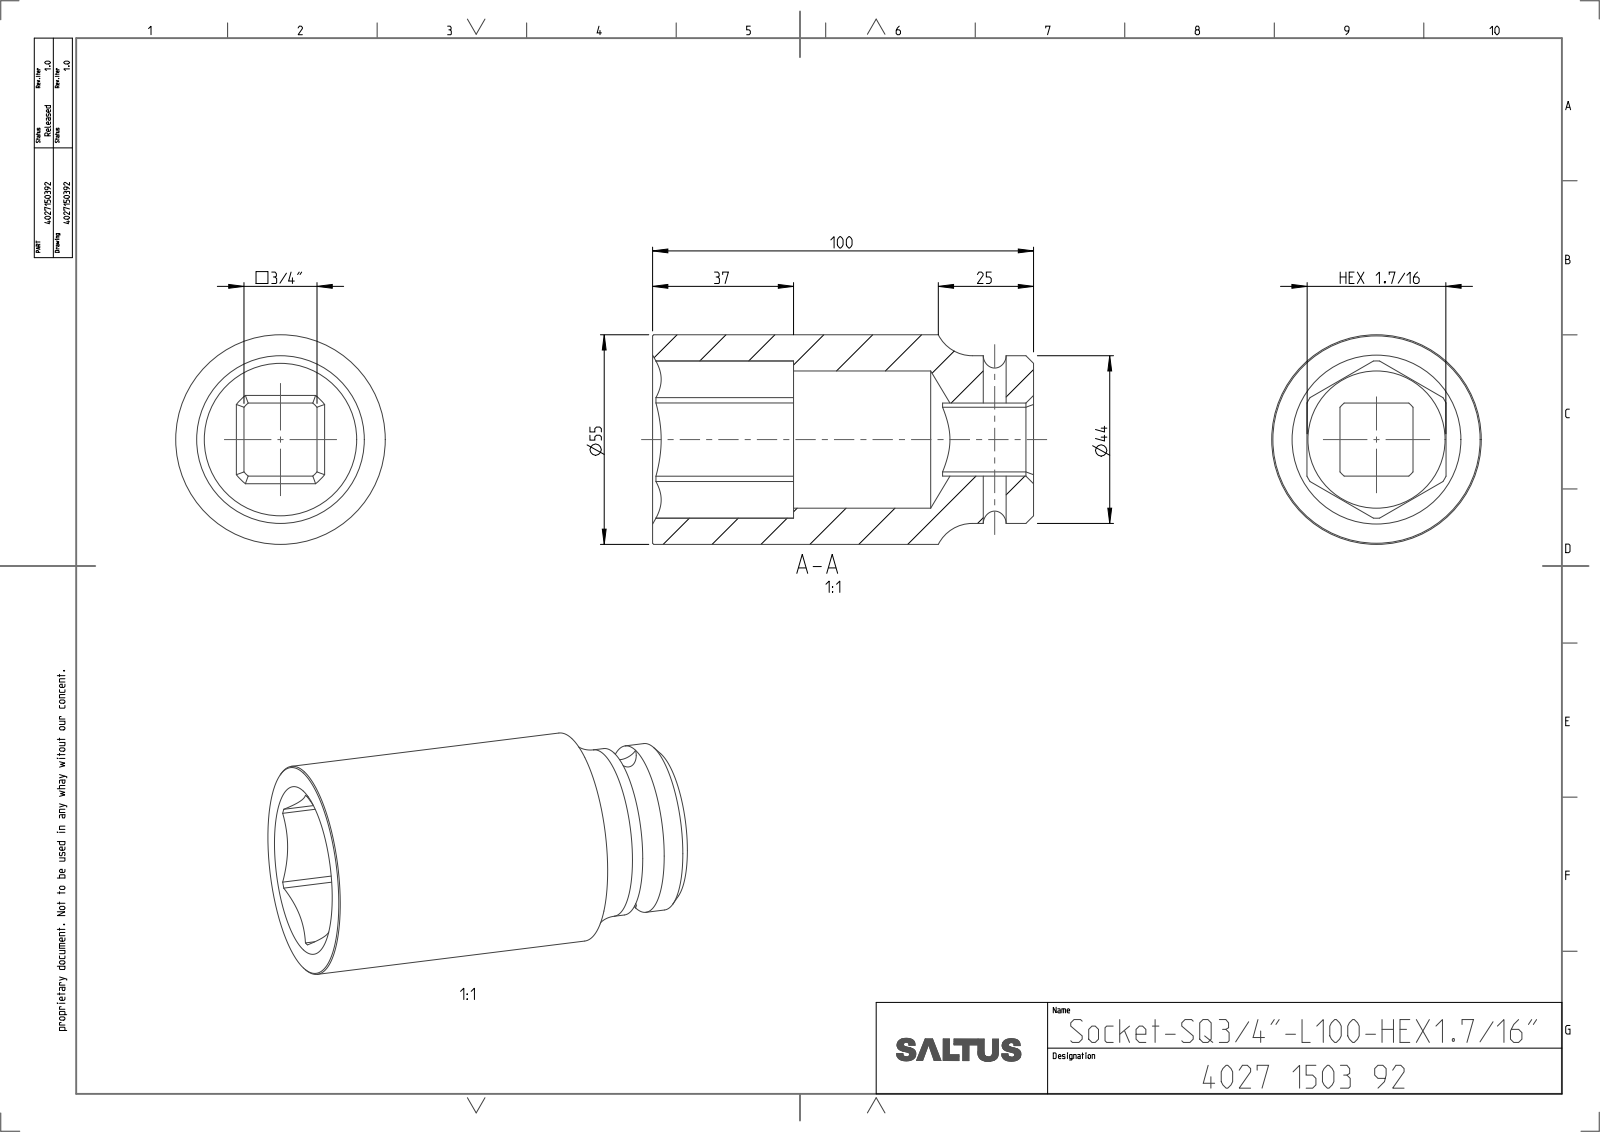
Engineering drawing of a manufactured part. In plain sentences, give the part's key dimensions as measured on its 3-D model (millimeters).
The part is named "4027150392". Its 3-D file was written by "CREO PARAMETRIC BY PTC INC, 2022414 (CONFIG_CONTROL_DESIGN)". It is 1 solid with 55 faces: 17 planar, 22 cylindrical and 16 other. Overall it measures 100 by 55 by 55 millimeters. Its volume is 124 633 cubic millimeters and its surface area 30 684 square millimeters. Round holes: 1 of diameter 6, 1 of diameter 36. Round bosses or shafts: 1 of diameter 55, 1 of diameter 44. Partial cylindrical surfaces (rounded edges, fillets, slot ends): 1 of radius 12.8, 1 of radius 20.63. The main face-to-face distances are 36.5, 100, 8.66, 27.84, 19.18, 63, 37.
